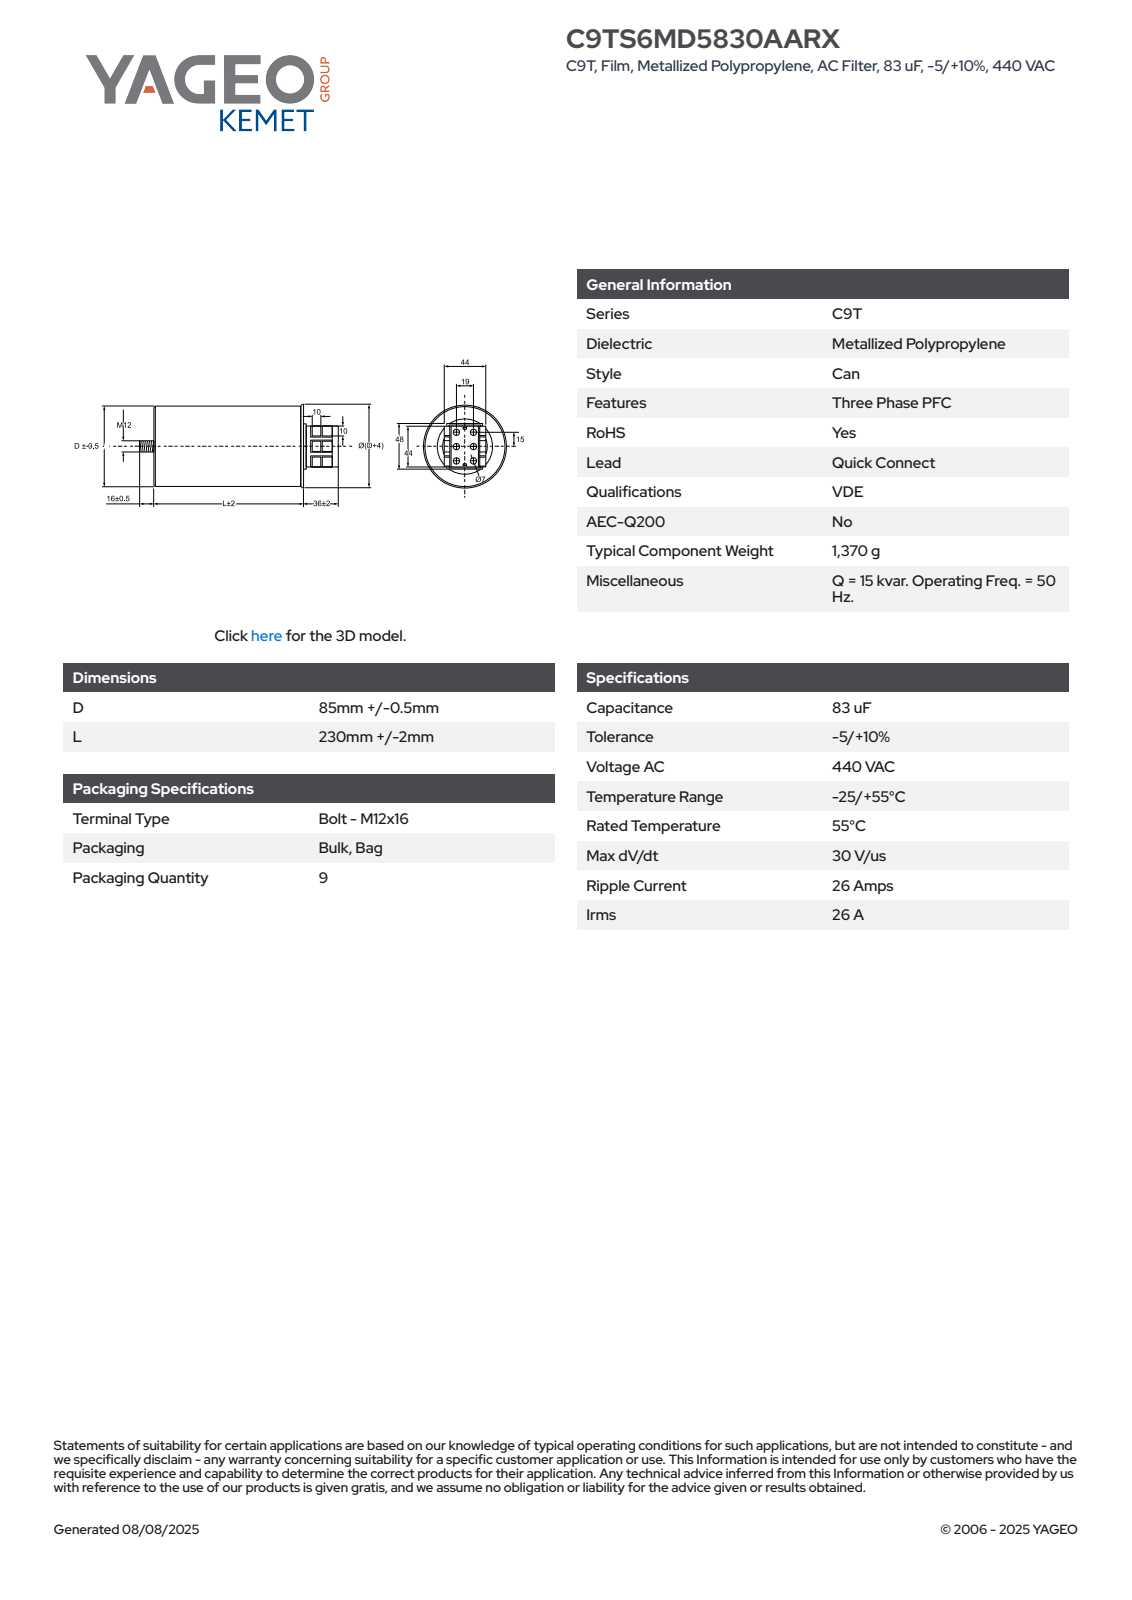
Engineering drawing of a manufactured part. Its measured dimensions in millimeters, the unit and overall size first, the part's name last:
Units: millimetres
Overall size (bounding box): 286.5 × 89.5 × 89.5
Round holes (diameter × count): ⌀7 ×6
Round bosses / shafts (diameter × count): ⌀85.5 ×1, ⌀12 ×1
Partial cylindrical surfaces — rounded edges, fillets, slot ends (radius × count): R42.76 ×1
Main face-to-face distances: 10, 232, 11.15, 15.85, 1.15, 4, 44, 236, 38, 17
Hole centre spacings: 15, 24.21, 19, 30, 35.51
Volume: 1 369 000 mm³ · Surface area: 96 104 mm²
Bodies: 1 solid, 138 faces (78 planar, 25 cylindrical, 35 other)
Part name (STEP PRODUCT): CFP_C9T_85X230_D85.5L232
STEP written by: SolidWorks 2014 (AUTOMOTIVE_DESIGN)
